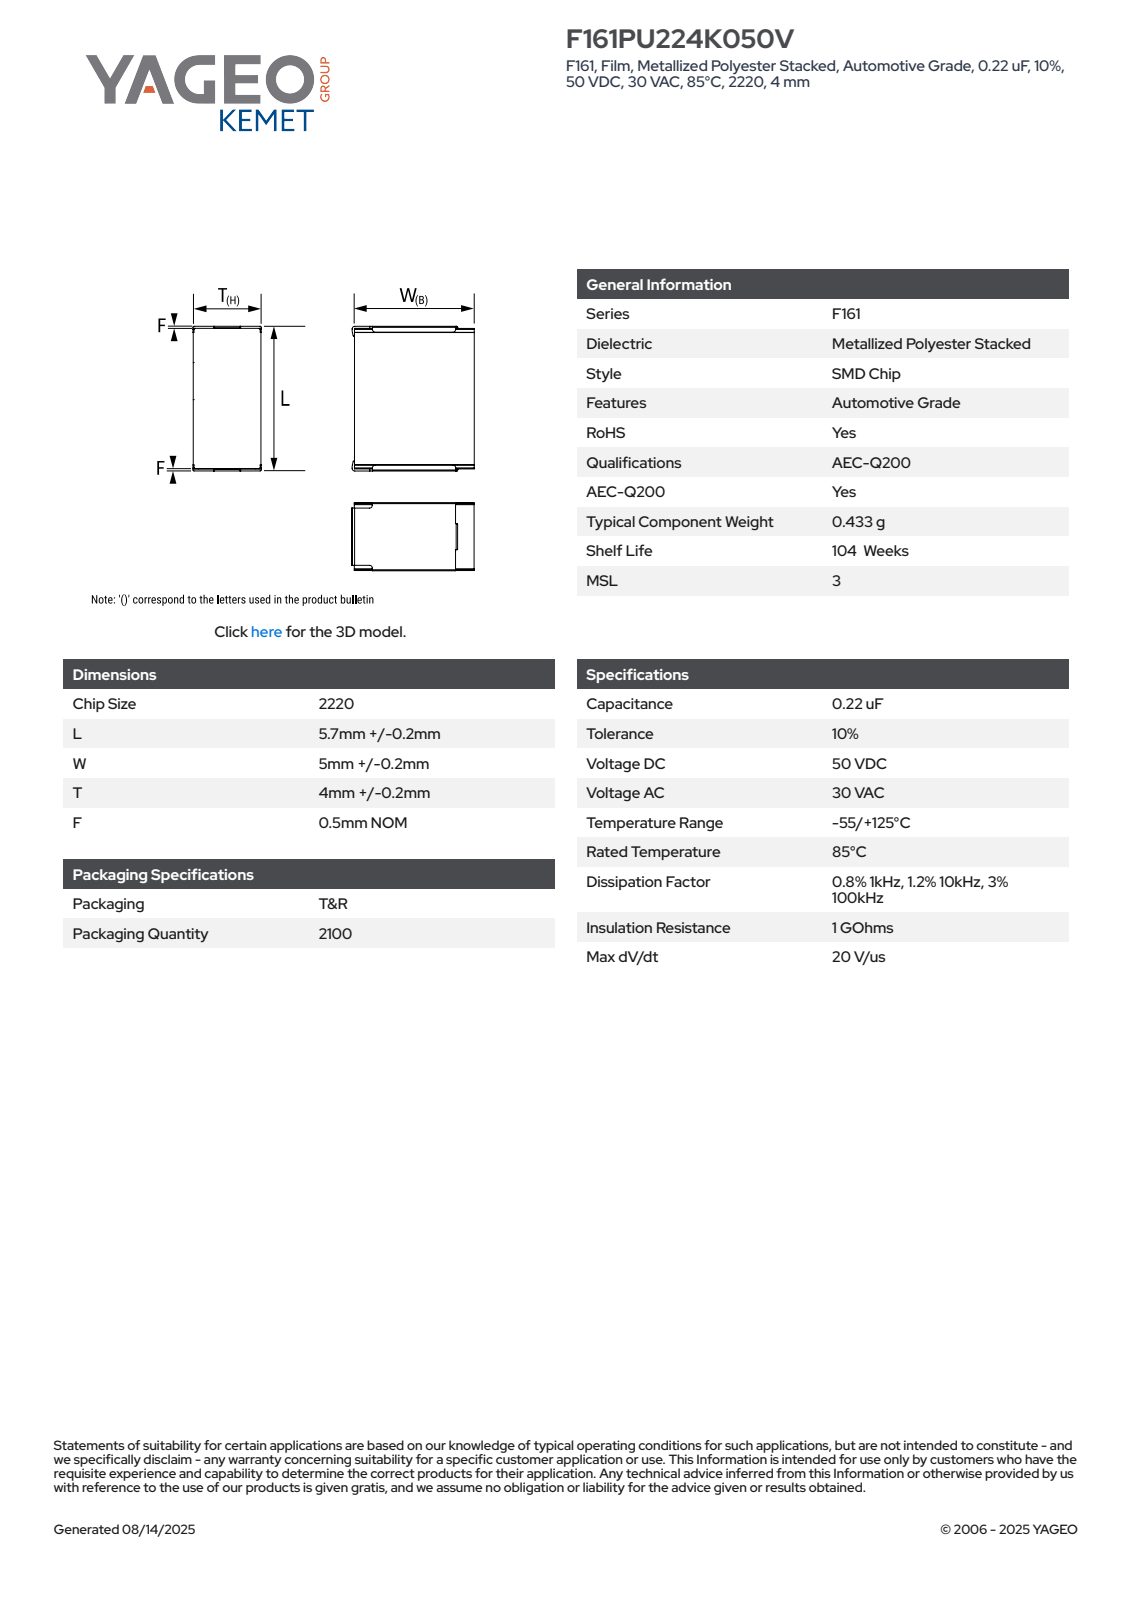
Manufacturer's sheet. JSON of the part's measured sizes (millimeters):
{"part_name": "CFS_KSTD_2220_L5.9W5.2T4.2F0.5", "step_written_by": "SolidWorks 2021 (AUTOMOTIVE_DESIGN)", "units": "millimeters", "bodies": {"solids": 4, "faces": 121, "planar": 107, "cylindrical": 14, "other": 0}, "overall_size": [5.9, 5.37, 4.42], "volume_mm3": 121, "surface_area_mm2": 160, "partial_cylinders_radius": [[0.25, 10], [0.21, 4]], "face_to_face_distances": [4.2, 4.99, 0.5, 5.9, 5.4, 4.9, 4.31, 4.42, 5.37, 0.38]}
